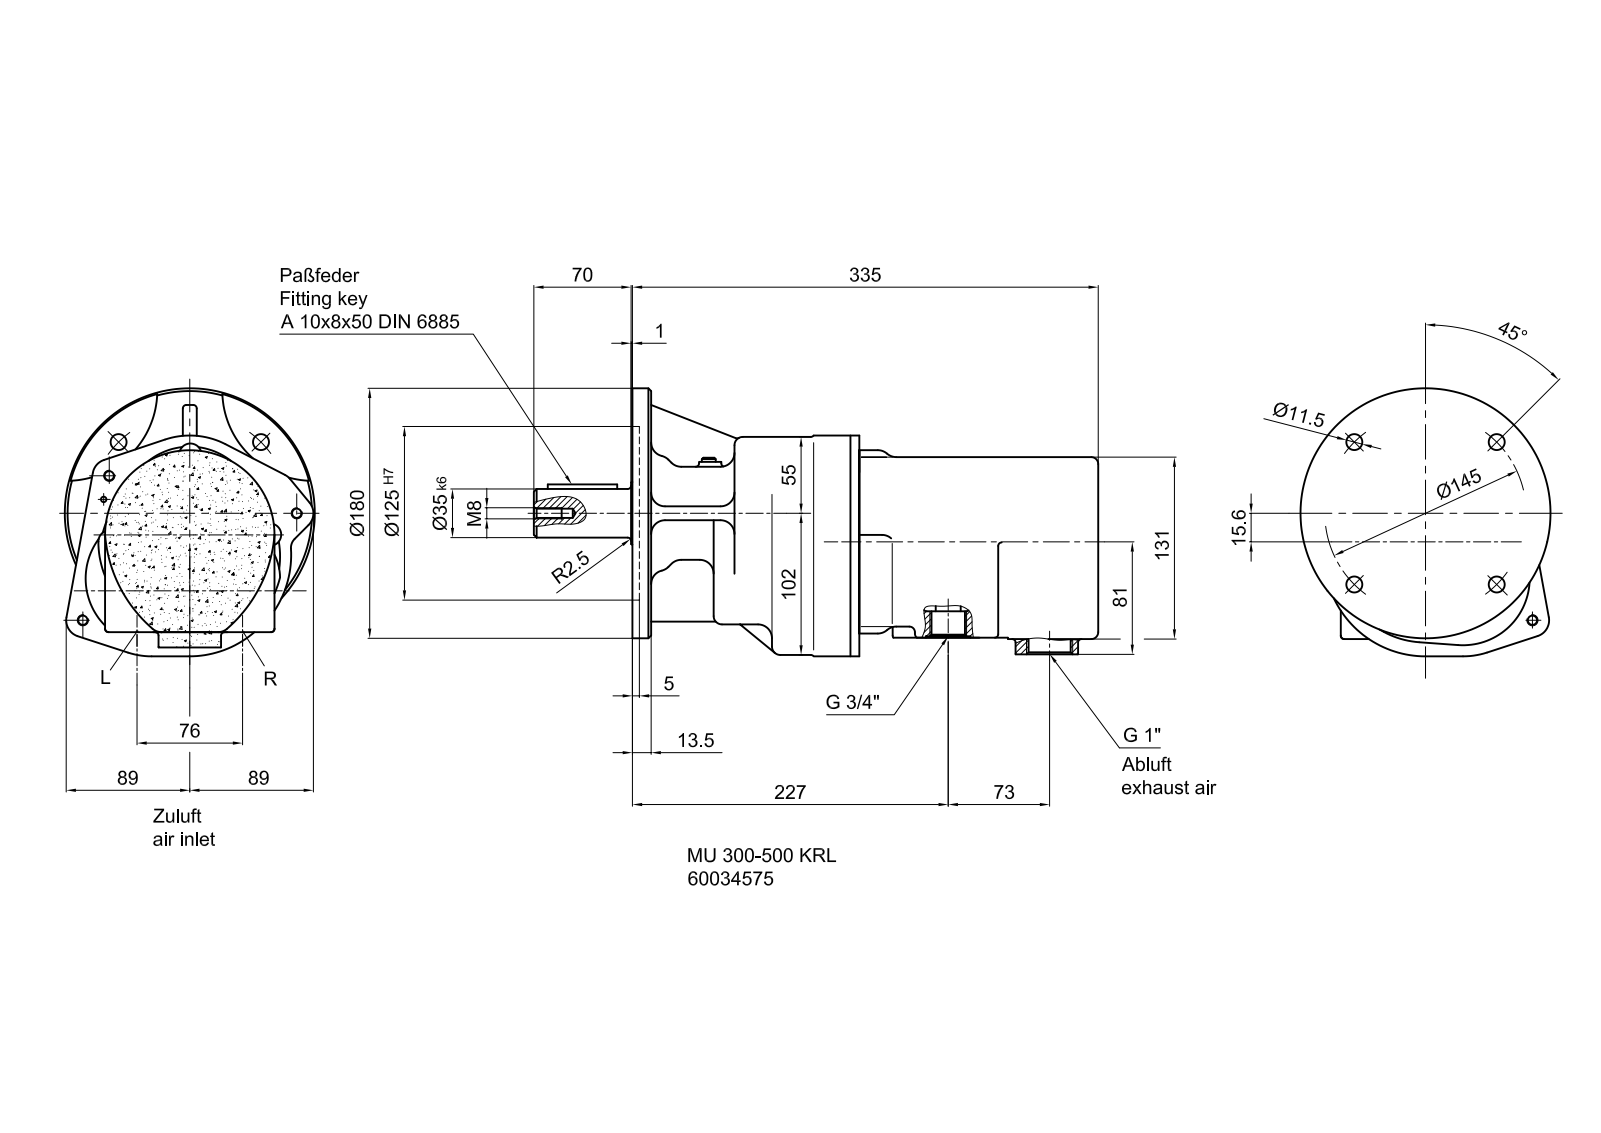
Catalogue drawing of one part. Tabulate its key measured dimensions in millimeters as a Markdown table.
| quantity | value |
| --- | --- |
| part name | MU 300-500 KRL_60034575 |
| STEP written by | Autodesk Inventor 2018 (CONFIG_CONTROL_DESIGN) |
| units | millimeters |
| bodies | 2 solids, 937 faces (331 planar, 323 cylindrical, 283 other) |
| overall size | 406.7 × 193 × 180 |
| volume | 4 573 000 mm³ |
| surface area | 302 982 mm² |
| round holes (diameter × count) | 4.92 × 4, 6.65 × 4, 11.5 × 4, 8.5 × 3, 9.5 × 3, 6.5 × 2, 24.12 × 2, 32 × 2, 2.5 × 1, 2.8 × 1, 3.9 × 1, 4 × 1 |
| round bosses / shafts (diameter × count) | 14.8 × 3, 13 × 3, 8 × 3, 180 × 1, 122 × 1, 45 × 1, 35 × 1, 16 × 1 |
| partial cylindrical surfaces (radius × count) | 2 × 30, 2.5 × 29, 4 × 20, 3 × 12, 6 × 12, 10 × 12, 1 × 6, 1.5 × 6 |
| main face-to-face distances | 5, 1, 335.9, 7.5, 330.9, 172, 158.9, 163.9, 322.4, 150.4 |
| hole center spacings | 30, 72.51, 81.71, 102.54, 57.36, 76, 138.14, 27.5 |
